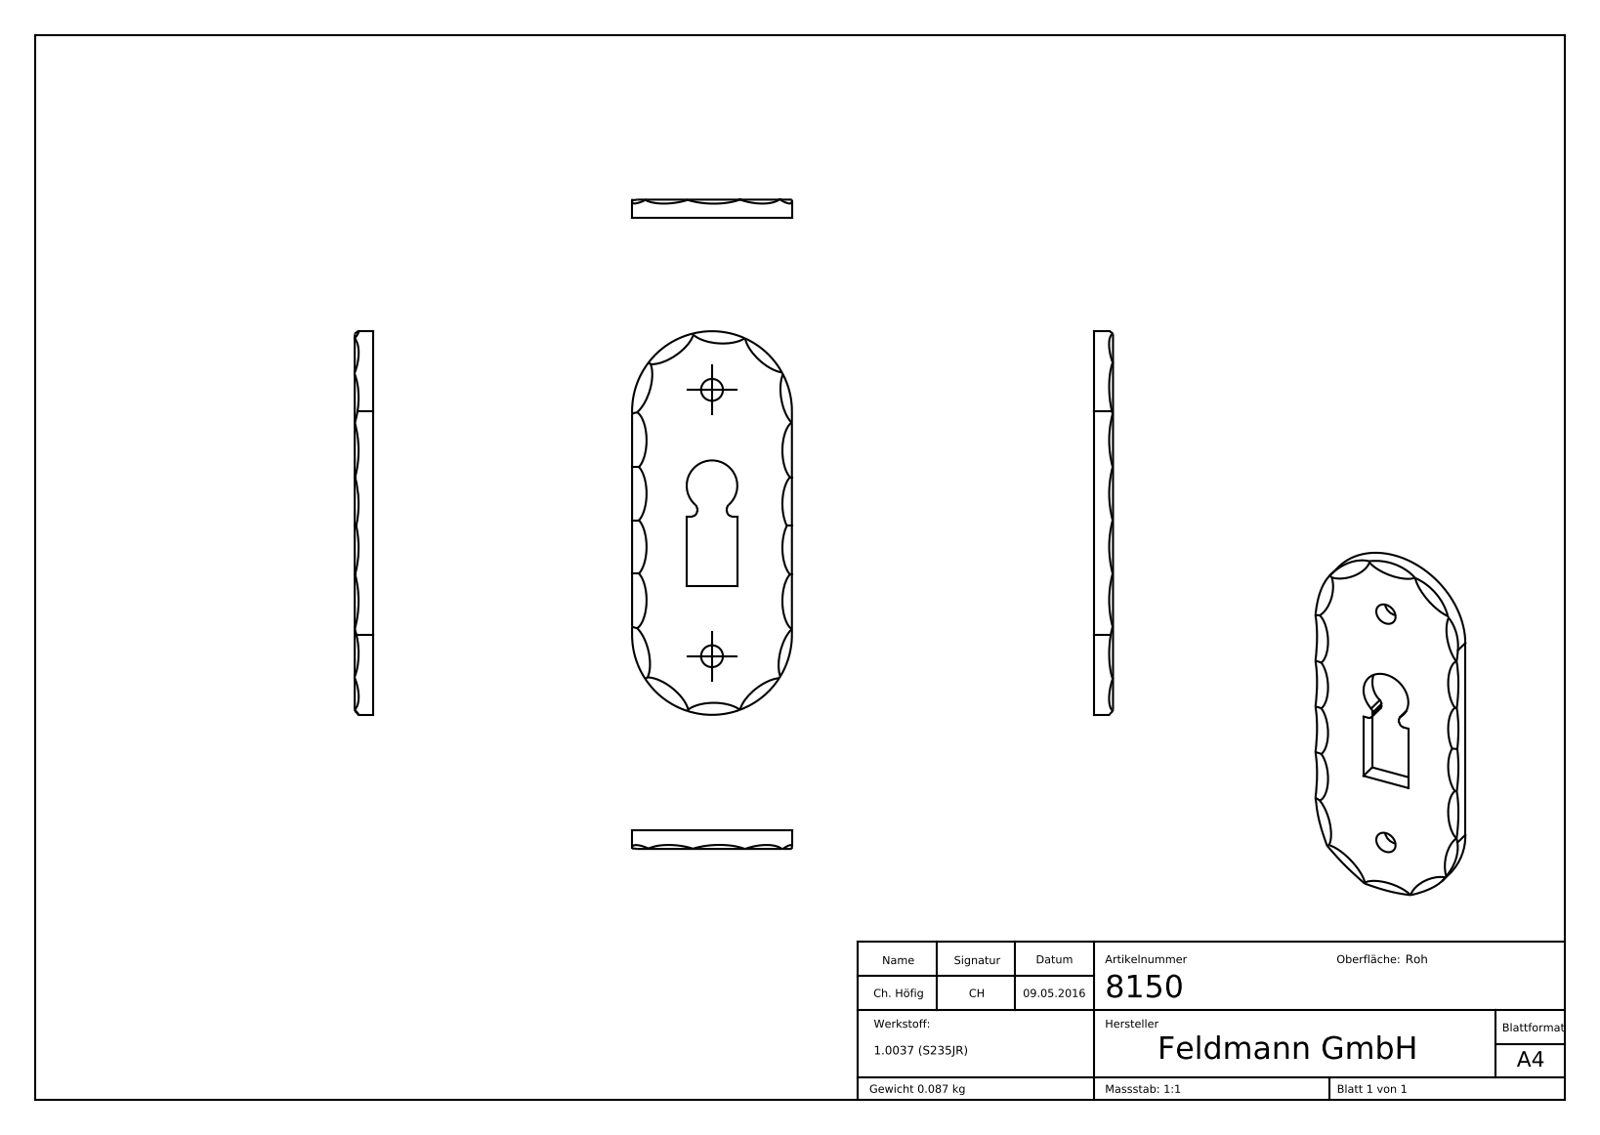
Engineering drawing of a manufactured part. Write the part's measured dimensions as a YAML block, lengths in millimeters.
part_name: "8150"
step_written_by: "SolidWorks 2015 (CONFIG_CONTROL_DESIGN)"
units: millimeters
bodies: {solids: 1, faces: 557, planar: 116, cylindrical: 159, other: 282}
overall_size: [72, 30, 3.7]
volume: 5756
surface_area: 4341
round_holes:
  - {diameter: 4.1, count: 2}
partial_cylinders:
  - {radius: 10, count: 19}
  - {radius: 1, count: 16}
  - {radius: 11.56, count: 7}
  - {radius: 11.56, count: 3}
  - {radius: 15, count: 2}
  - {radius: 4.75, count: 1}
face_to_face_distances: [3.5, 30, 10.25, 19.75, 9.5, 13, 1.95, 12.2, 17.8, 7.55]
hole_center_spacings: [50]
